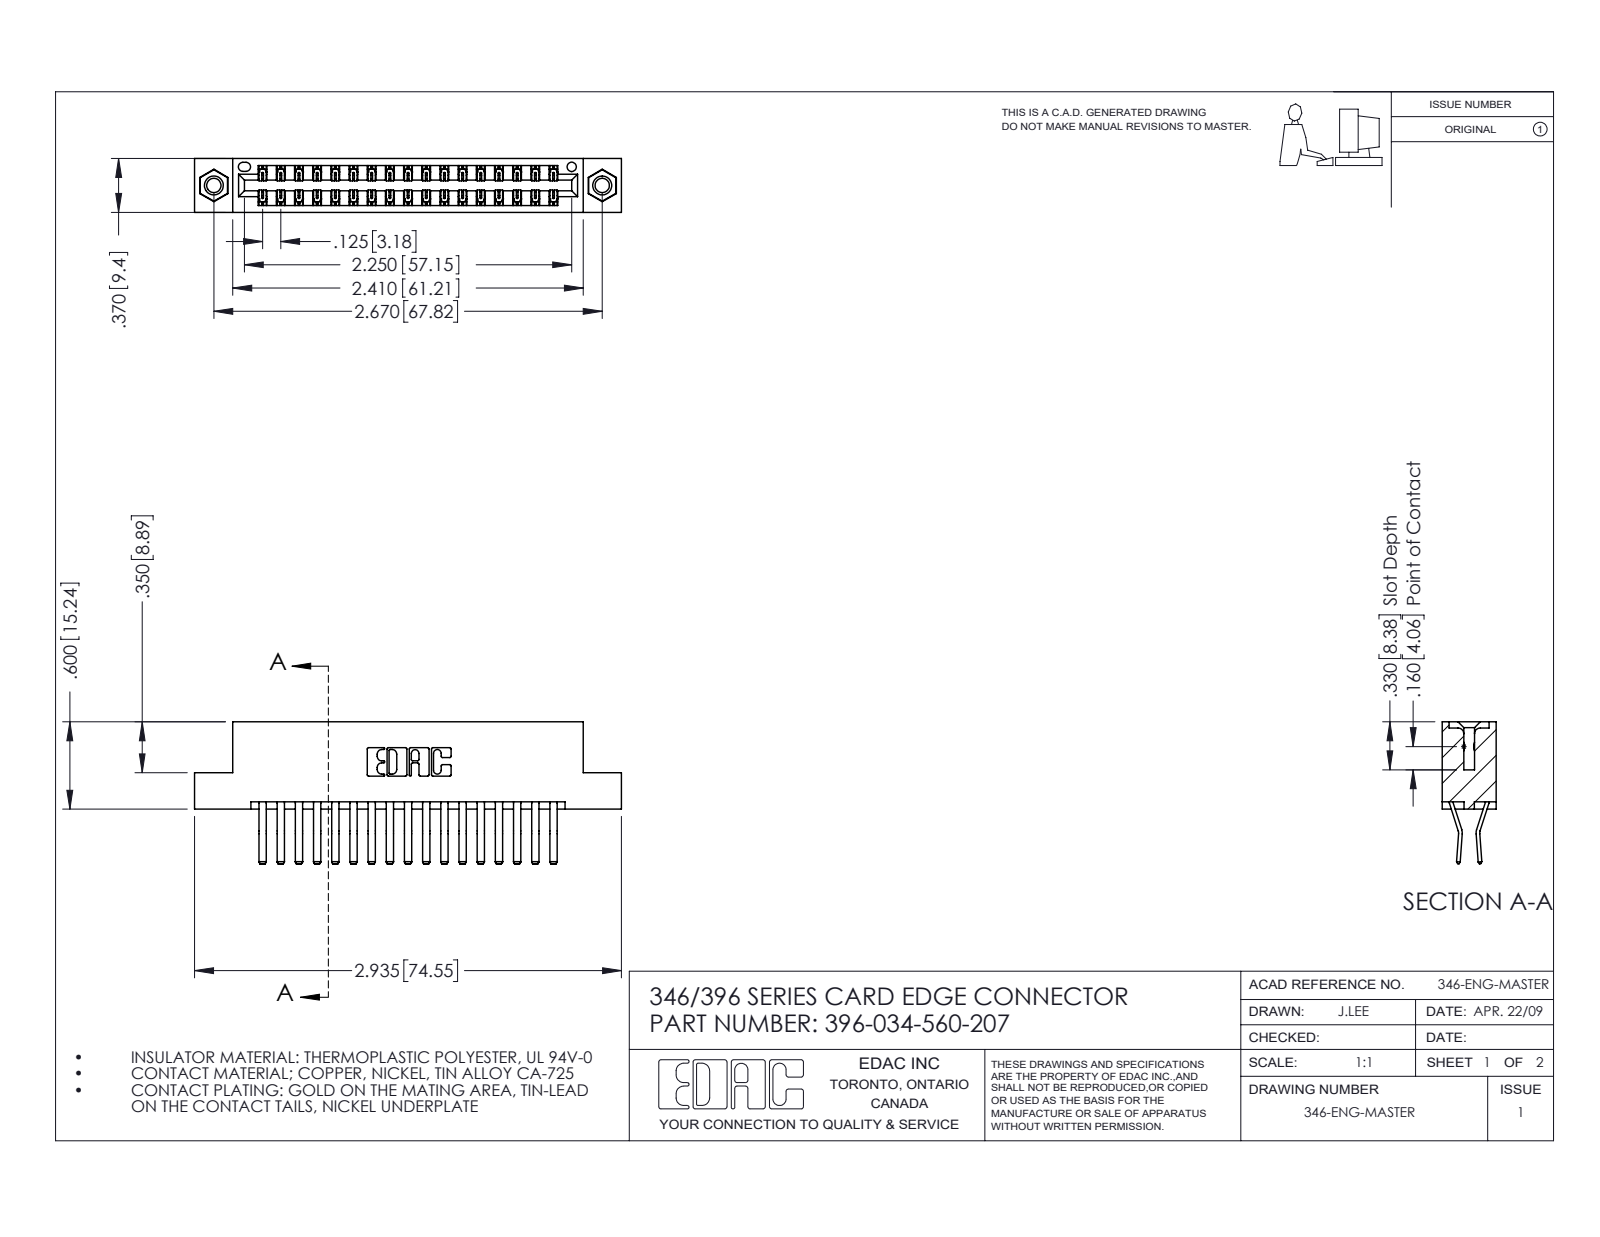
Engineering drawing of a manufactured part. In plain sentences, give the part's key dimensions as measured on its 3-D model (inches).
The part is named "345-292-001_560 Tail; 396-034-560-207; 345-250-001_345-250-005-103; 346 Part_Flush Mounting Lugs - 0.156 Dia-TI". Its 3-D file was written by "SolidWorks 2016 (CONFIG_CONTROL_DESIGN)". It is 37 solids with 2018 faces: 1298 planar, 704 cylindrical and 16 other. Overall it measures 2.935 by 0.975 by 0.37 inches. Its volume is 0.445 cubic inches and its surface area 15.89 square inches. Round holes: 2 of diameter 0.098, 2 of diameter 0.125, 2 of diameter 0.156, 1 of diameter 0.064. Round bosses or shafts: 2 of diameter 0.155. Partial cylindrical surfaces (rounded edges, fillets, slot ends): 51 of radius 0.006, 22 of radius 0.01, 6 of radius 0.007, 6 of radius 0.031, 3 of radius 0.026, 2 of radius 0.01, 2 of radius 0.014, 2 of radius 0.022. The main face-to-face distances are 0.048, 0.322, 0.25, 0.37, 0.025, 0.072, 0.298, 0.275, 0.148, 0.222. The hole center spacings are 0.246, 2.463, 2.67.
